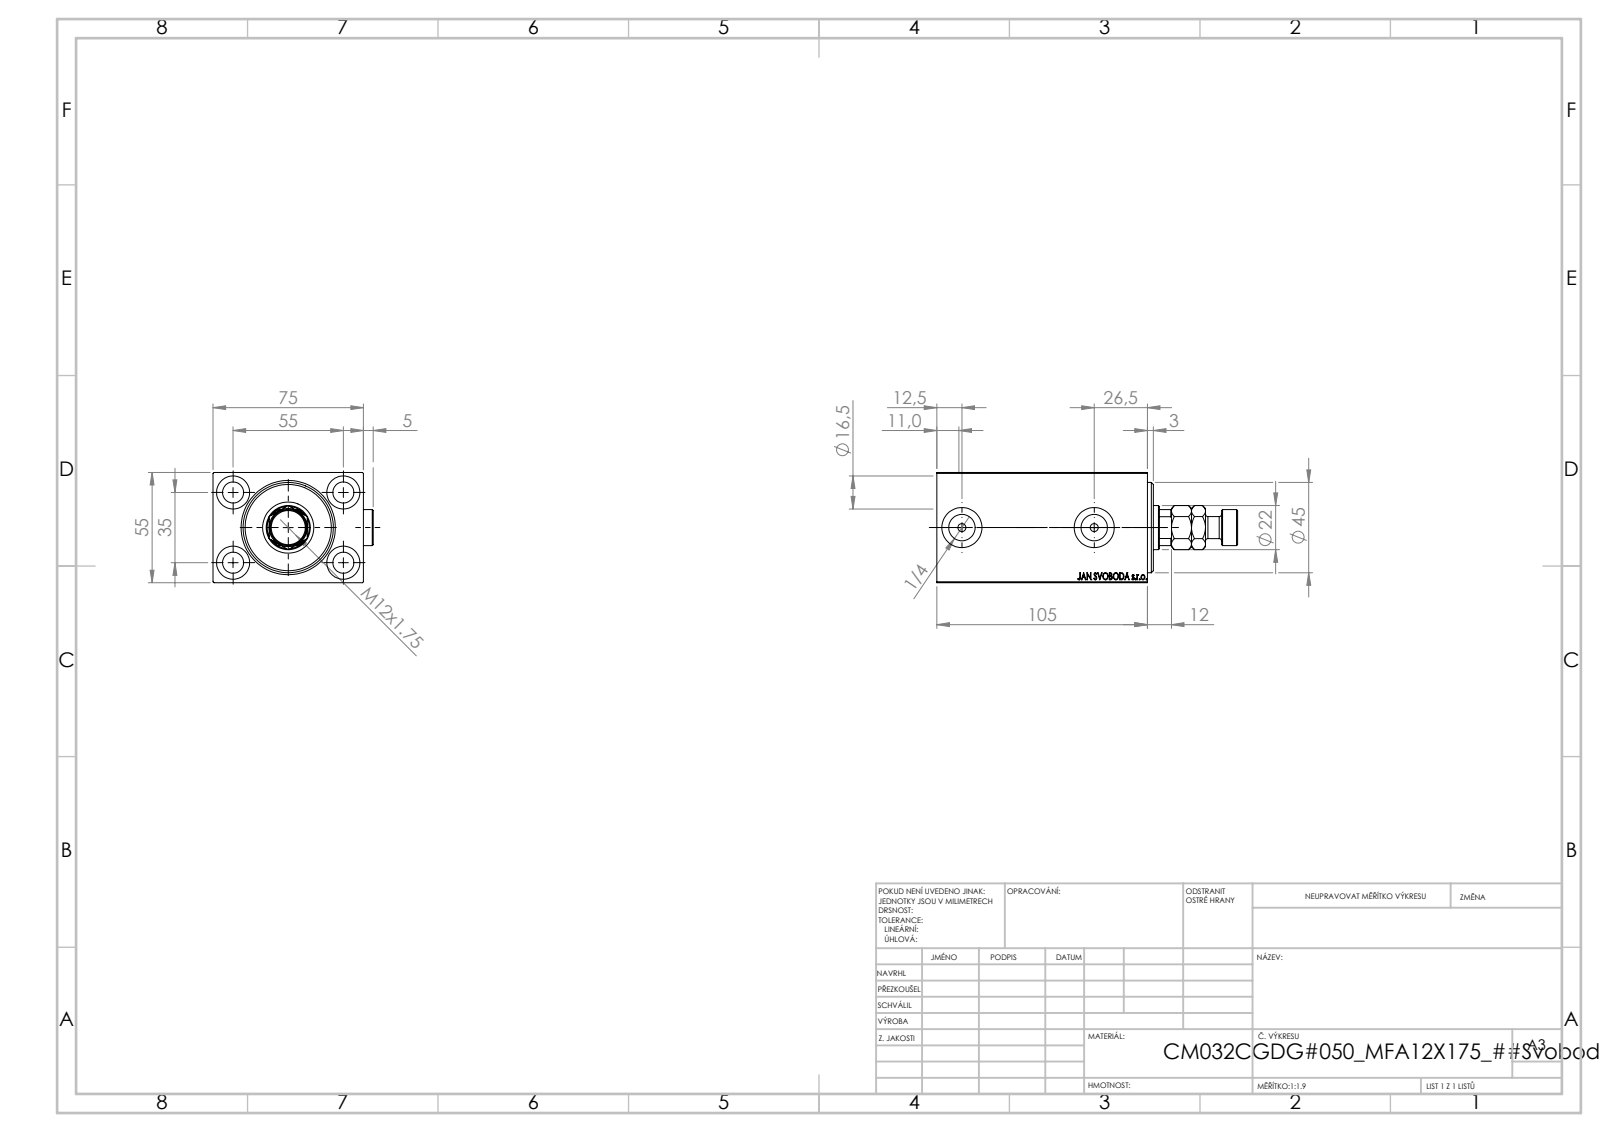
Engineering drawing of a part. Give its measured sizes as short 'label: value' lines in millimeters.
name: Zatka_OIL_PORT; MFA; V450CM_C_Body; V450CM_C_VCP (+1 more)
written by: SolidWorks 2019 (CONFIG_CONTROL_DESIGN)
unit: mm
bodies: 6 solids, 968 faces (458 planar, 80 cylindrical, 430 other)
size: 150 × 79.9 × 55
volume: 372 864 mm³; area: 82 800 mm²
holes: 5× ⌀10.5, 4× ⌀16.5, 2× ⌀4, 2× ⌀13.16, 2× ⌀20, 1× ⌀22, 1× ⌀25.5, 1× ⌀32, 1× ⌀34, 1× ⌀45
bosses: 3× ⌀18, 1× ⌀11
rounds: 1× R10.5
face distances: 55, 75, 5, 10, 95, 105, 100, 90, 74.9, 83
hole spacings: 32.6, 35, 55, 65.19, 66
